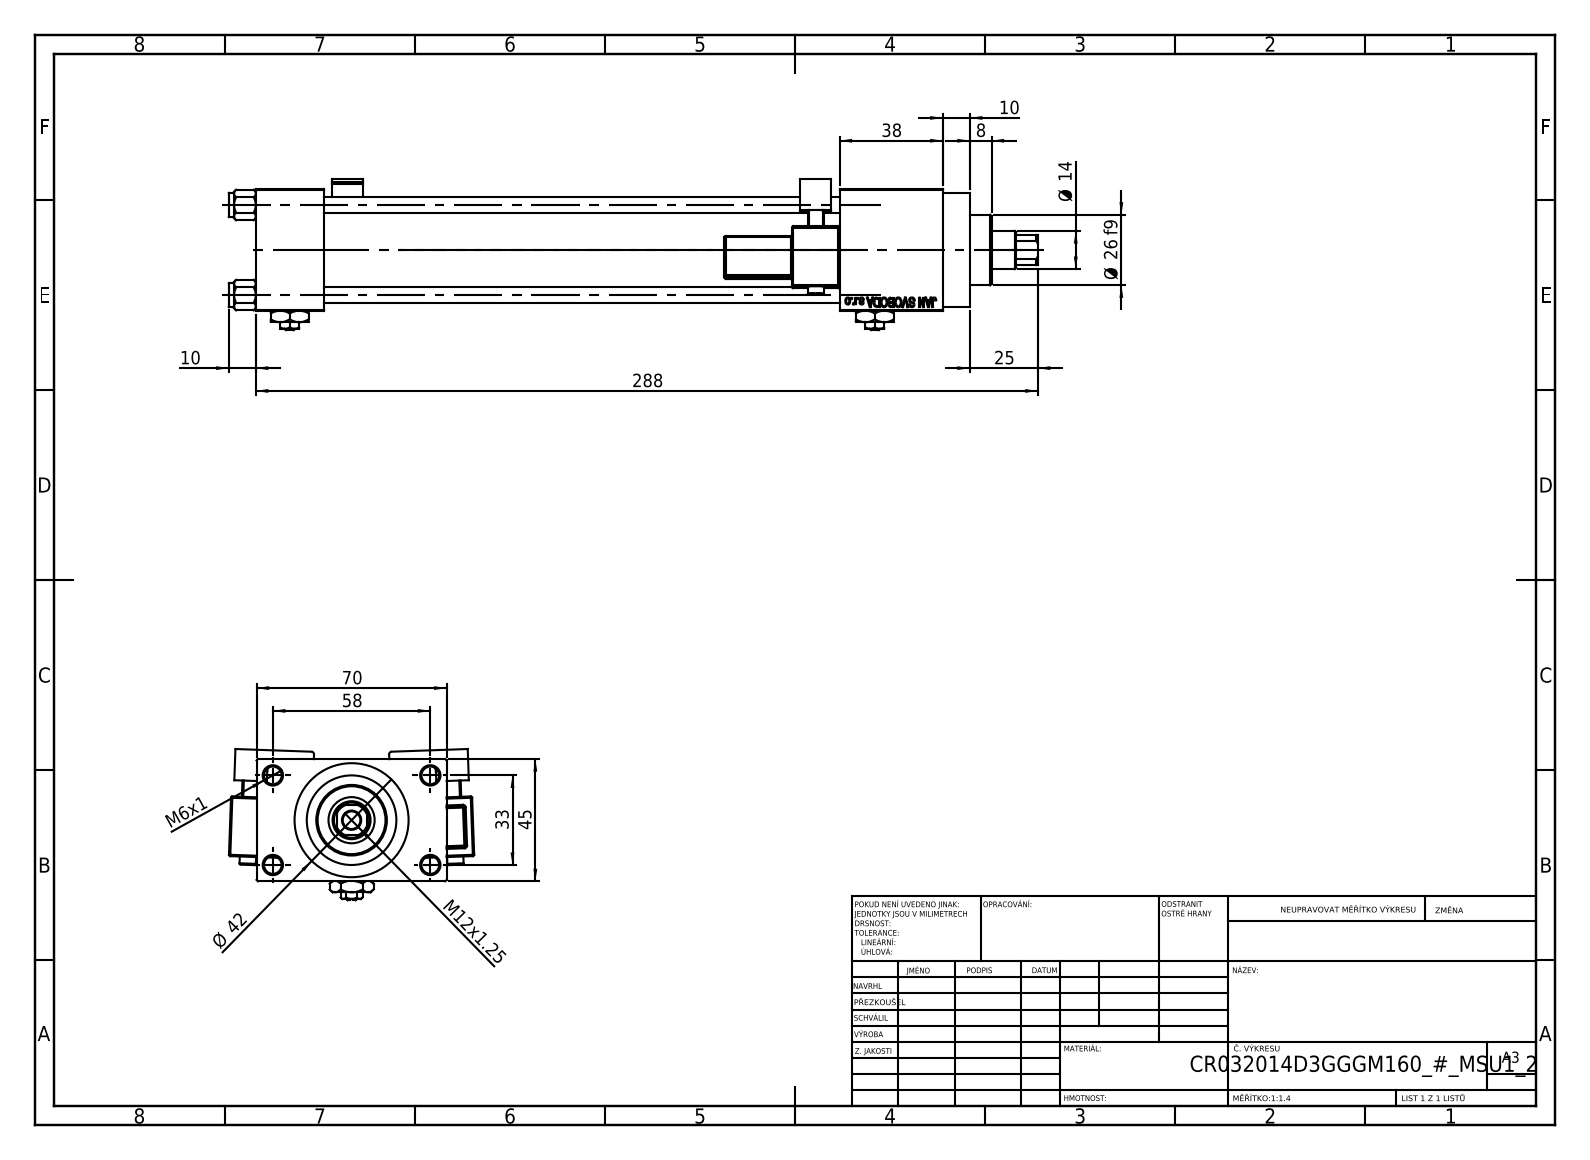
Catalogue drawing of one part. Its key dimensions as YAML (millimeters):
part_name: "V215CR_VCP_D; Zatka_pro_OIL_PORT; NUT_M5_D; V215CR_D_Body (+3 more)"
step_written_by: "SolidWorks 2019 (CONFIG_CONTROL_DESIGN)"
units: millimeters
bodies: {solids: 15, faces: 1360, planar: 604, cylindrical: 160, other: 596}
overall_size: [298, 90.31, 55.72]
volume: 354922
surface_area: 136118
round_holes:
  - {diameter: 6.5, count: 5}
  - {diameter: 6, count: 4}
  - {diameter: 7, count: 2}
  - {diameter: 13.16, count: 2}
  - {diameter: 20, count: 2}
  - {diameter: 14, count: 1}
  - {diameter: 17, count: 1}
  - {diameter: 24, count: 1}
  - {diameter: 32, count: 1}
  - {diameter: 33, count: 1}
round_bosses_or_shafts:
  - {diameter: 9, count: 4}
  - {diameter: 6, count: 2}
  - {diameter: 42, count: 1}
  - {diameter: 38, count: 1}
  - {diameter: 26, count: 1}
partial_cylinders:
  - {radius: 0.5, count: 48}
  - {radius: 1, count: 2}
  - {radius: 2.5, count: 2}
  - {radius: 4, count: 2}
  - {radius: 6.5, count: 1}
face_to_face_distances: [45, 25, 12.5, 190, 3, 57.5, 215, 228, 38, 70]
hole_center_spacings: [12.4, 23.48, 33.2, 33.37, 35.35, 45.6, 56.35, 33]
